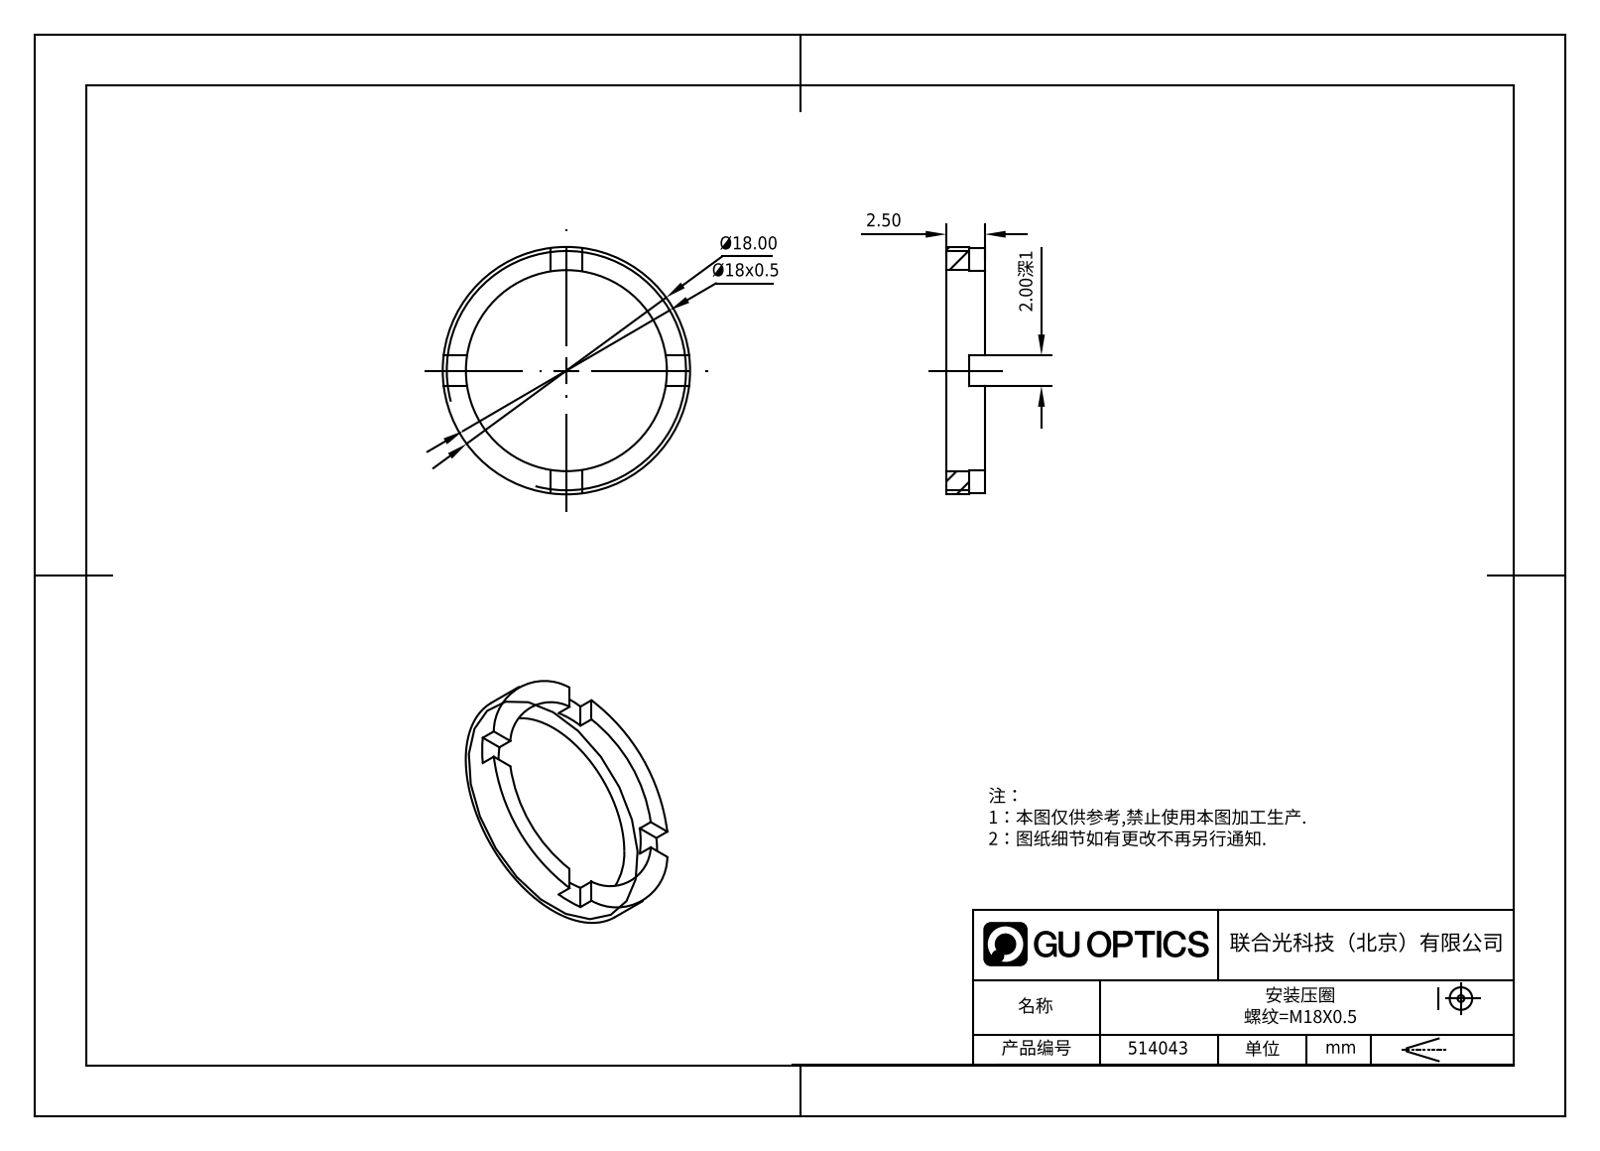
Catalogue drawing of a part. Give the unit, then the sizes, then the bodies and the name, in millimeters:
Units: millimetres
Overall size (bounding box): 18 × 18 × 2.5
Round holes (diameter × count): ⌀15 ×1
Round bosses / shafts (diameter × count): ⌀18 ×1
Main face-to-face distances: 2.5, 1.5, 1, 2
Volume: 182 mm³ · Surface area: 411 mm²
Bodies: 1 solid, 21 faces (17 planar, 4 cylindrical, 0 other)
Part name (STEP PRODUCT): 514043
STEP written by: SolidWorks 2020 (CONFIG_CONTROL_DESIGN)
